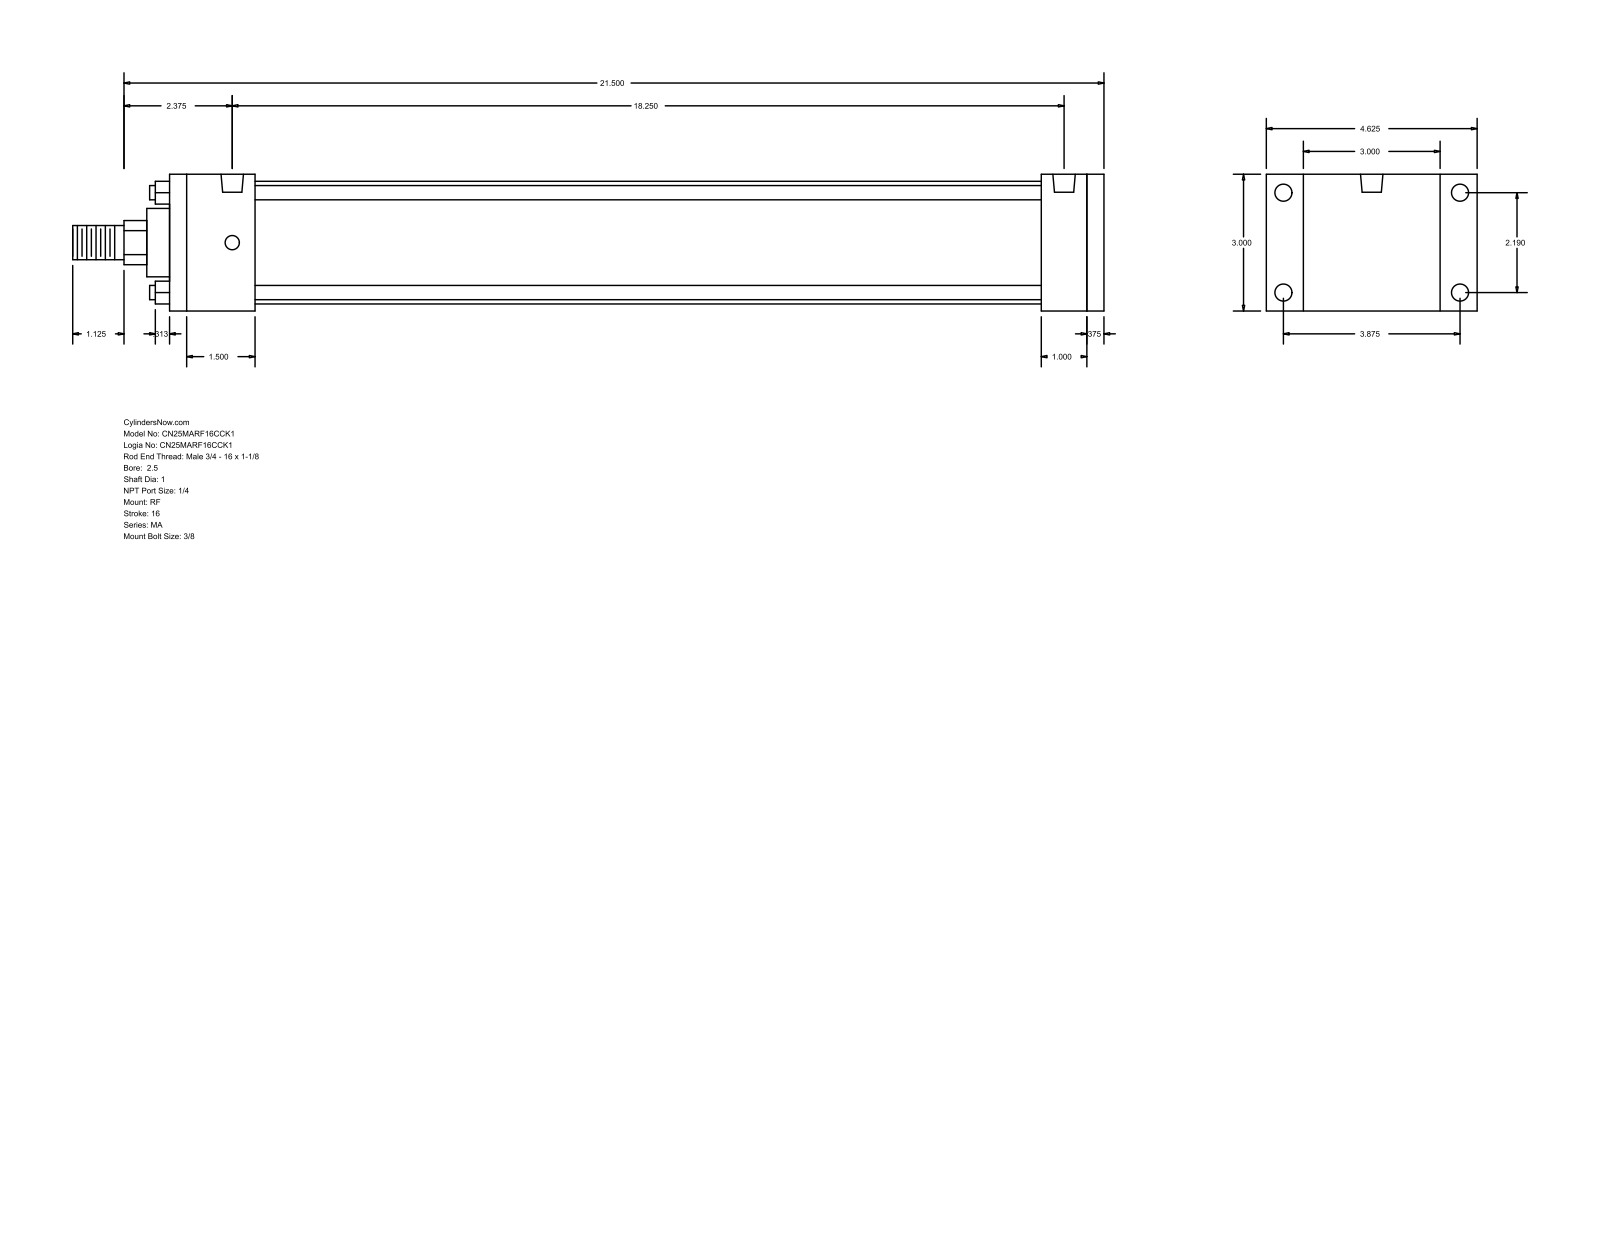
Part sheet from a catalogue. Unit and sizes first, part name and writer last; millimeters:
Units: millimetres
Overall size (bounding box): 574.67 × 117.47 × 76.2
Round holes (diameter × count): ⌀7.94 ×4, ⌀9.53 ×4, ⌀12.49 ×2
Round bosses / shafts (diameter × count): ⌀7.94 ×4, ⌀68.33 ×1, ⌀38.1 ×1, ⌀25.4 ×1, ⌀19.05 ×1
Partial cylindrical surfaces — rounded edges, fillets, slot ends (radius × count): R12.29 ×1
Main face-to-face distances: 76.2, 520.7, 511.18, 9.52, 25.4, 47.63, 485.78, 438.15, 463.55, 473.07
Hole centre spacings: 55.62, 98.42, 113.05, 463.55
Bodies: 0 solids, 92 faces (64 planar, 28 cylindrical, 0 other)
Part name (STEP PRODUCT): MA_RF__0250_1
STEP written by: GSSL Pune (CONFIG_CONTROL_DESIGN)
